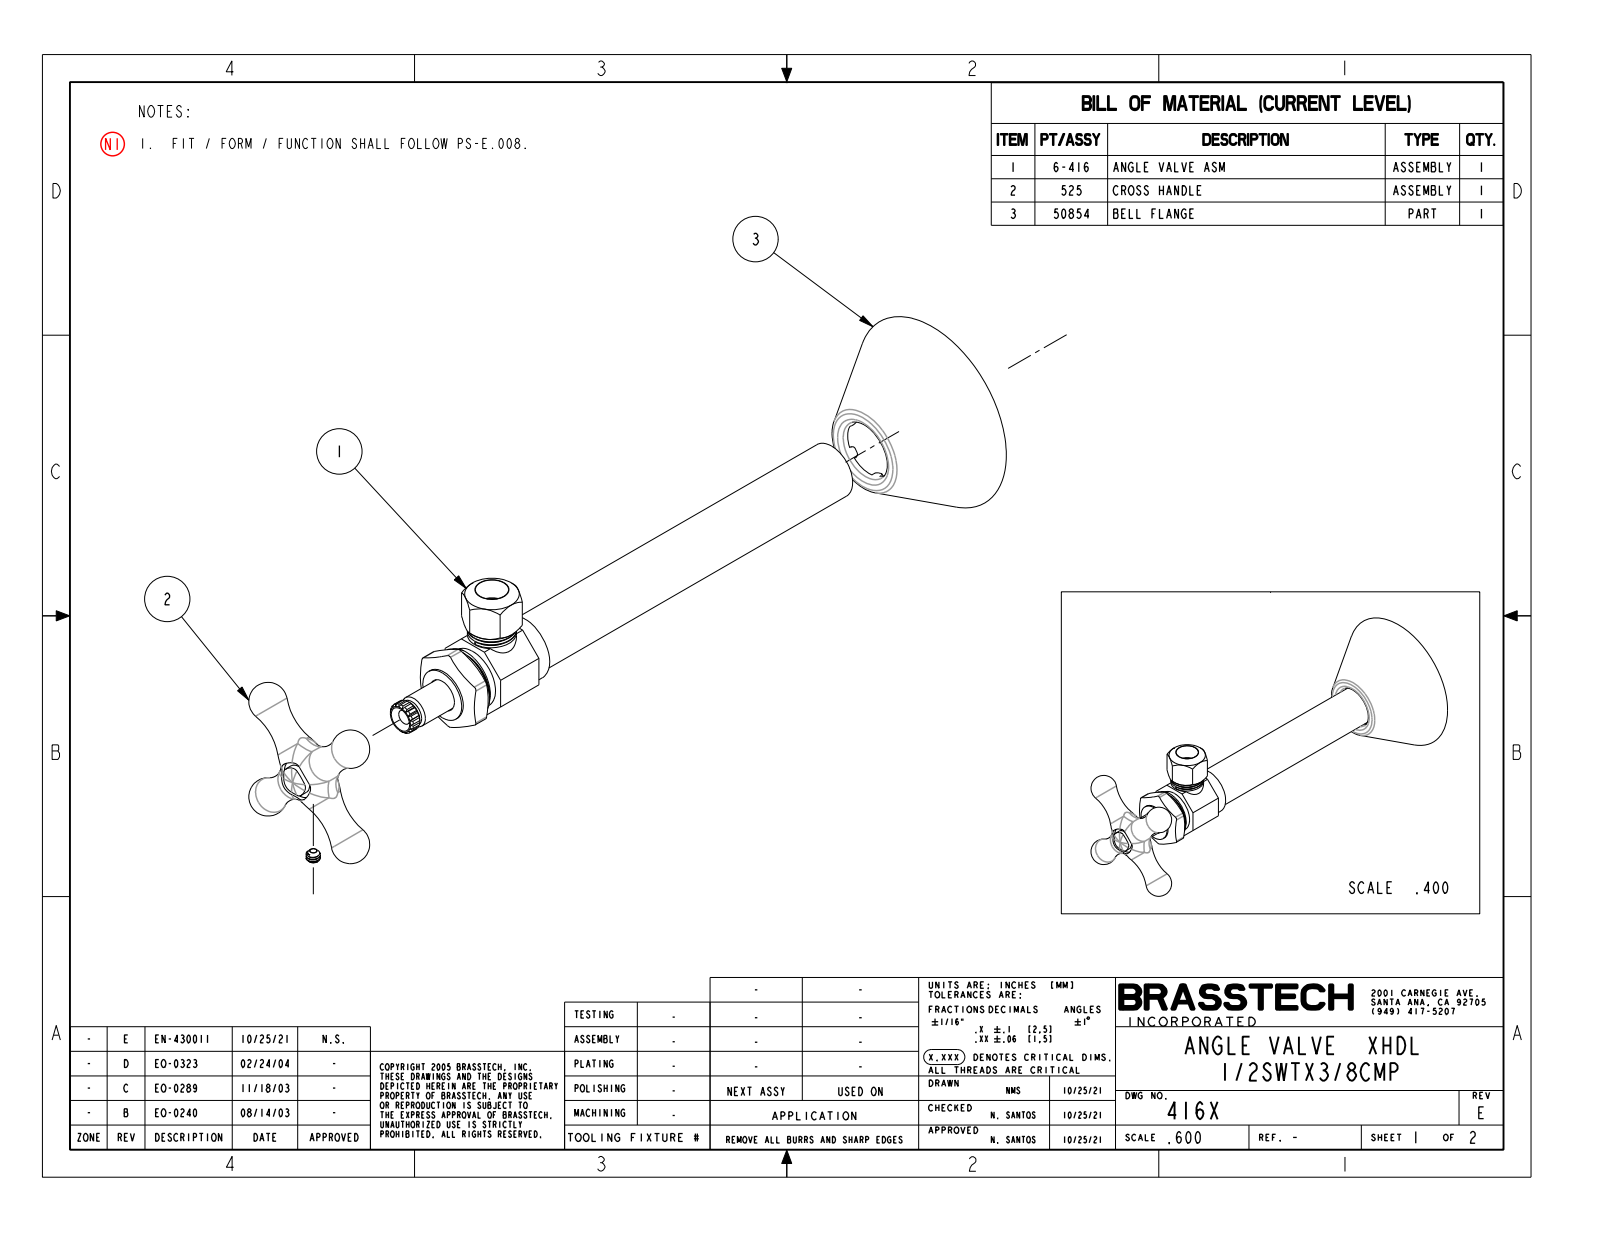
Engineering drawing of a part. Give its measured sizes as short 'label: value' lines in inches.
name: 416X
written by: CREO PARAMETRIC BY PTC INC, 2018500 (CONFIG_CONTROL_DESIGN)
unit: in
bodies: 4 solids, 721 faces (186 planar, 243 cylindrical, 292 other)
size: 7.144 × 2.4 × 2.4
volume: 2.046 in³; area: 94.26 in²
holes: 1× ⌀0.13, 1× ⌀0.175, 1× ⌀0.392, 1× ⌀0.4, 1× ⌀0.464, 1× ⌀0.48, 1× ⌀0.517, 1× ⌀0.563, 1× ⌀0.68, 1× ⌀0.735, 1× ⌀0.758, 1× ⌀0.8
bosses: 1× ⌀0.86, 1× ⌀0.753, 1× ⌀0.63, 1× ⌀0.629, 1× ⌀0.62, 1× ⌀0.54, 1× ⌀0.38, 1× ⌀0.376
rounds: 18× R0.01, 6× R0.05, 1× R0.17, 1× R0.186, 1× R0.187
face distances: 0.9, 0.625, 0.137, 0.763, 4.39, 0.887, 0.875, 0.125, 5.005, 0.615
hole spacings: 1.293
